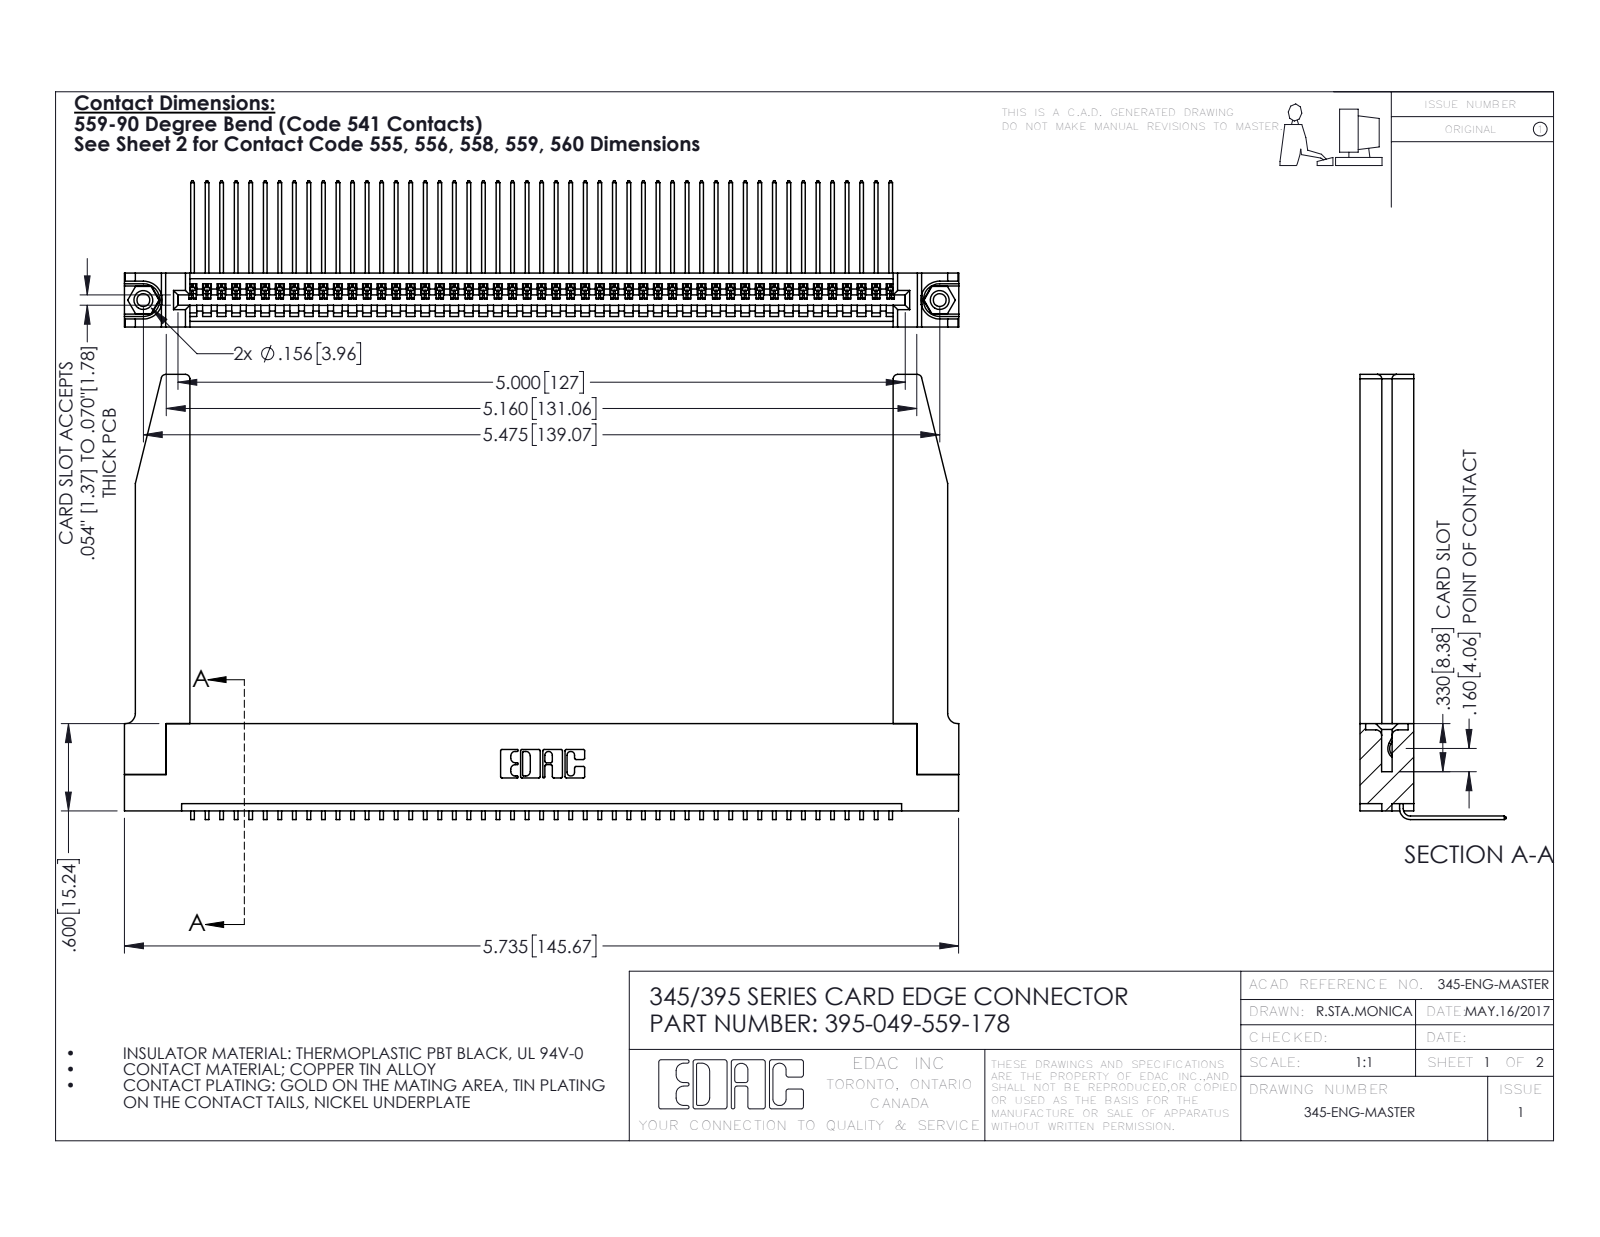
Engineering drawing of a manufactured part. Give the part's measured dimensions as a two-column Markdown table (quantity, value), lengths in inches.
| quantity | value |
| --- | --- |
| part name | 345-220-078_345-220-078; 345 Part_Flush Mounting Lugs - 0.156 Dia-TH; 395-049-559-178; 345-292-001_558 559 Tail - 1 (+1 more) |
| STEP written by | SolidWorks 2016 (CONFIG_CONTROL_DESIGN) |
| units | inches |
| bodies | 54 solids, 3300 faces (2280 planar, 968 cylindrical, 52 other) |
| overall size | 5.736 × 3.059 × 1.005 |
| volume | 1.332 in³ |
| surface area | 41.2 in² |
| round holes (diameter × count) | 0.089 × 2, 0.125 × 2, 0.156 × 2, 0.064 × 1 |
| round bosses / shafts (diameter × count) | 0.155 × 2 |
| partial cylindrical surfaces (radius × count) | 0.006 × 98, 0.01 × 22, 0.03 × 8, 0.007 × 6, 0.031 × 6, 0.026 × 3, 0.031 × 2, 0.04 × 2 |
| main face-to-face distances | 0.37, 0.072, 0.298, 0.2, 0.098, 0.272, 0.025, 0.225, 0.148, 0.15 |
| hole center spacings | 0.27, 5.239, 5.475 |
